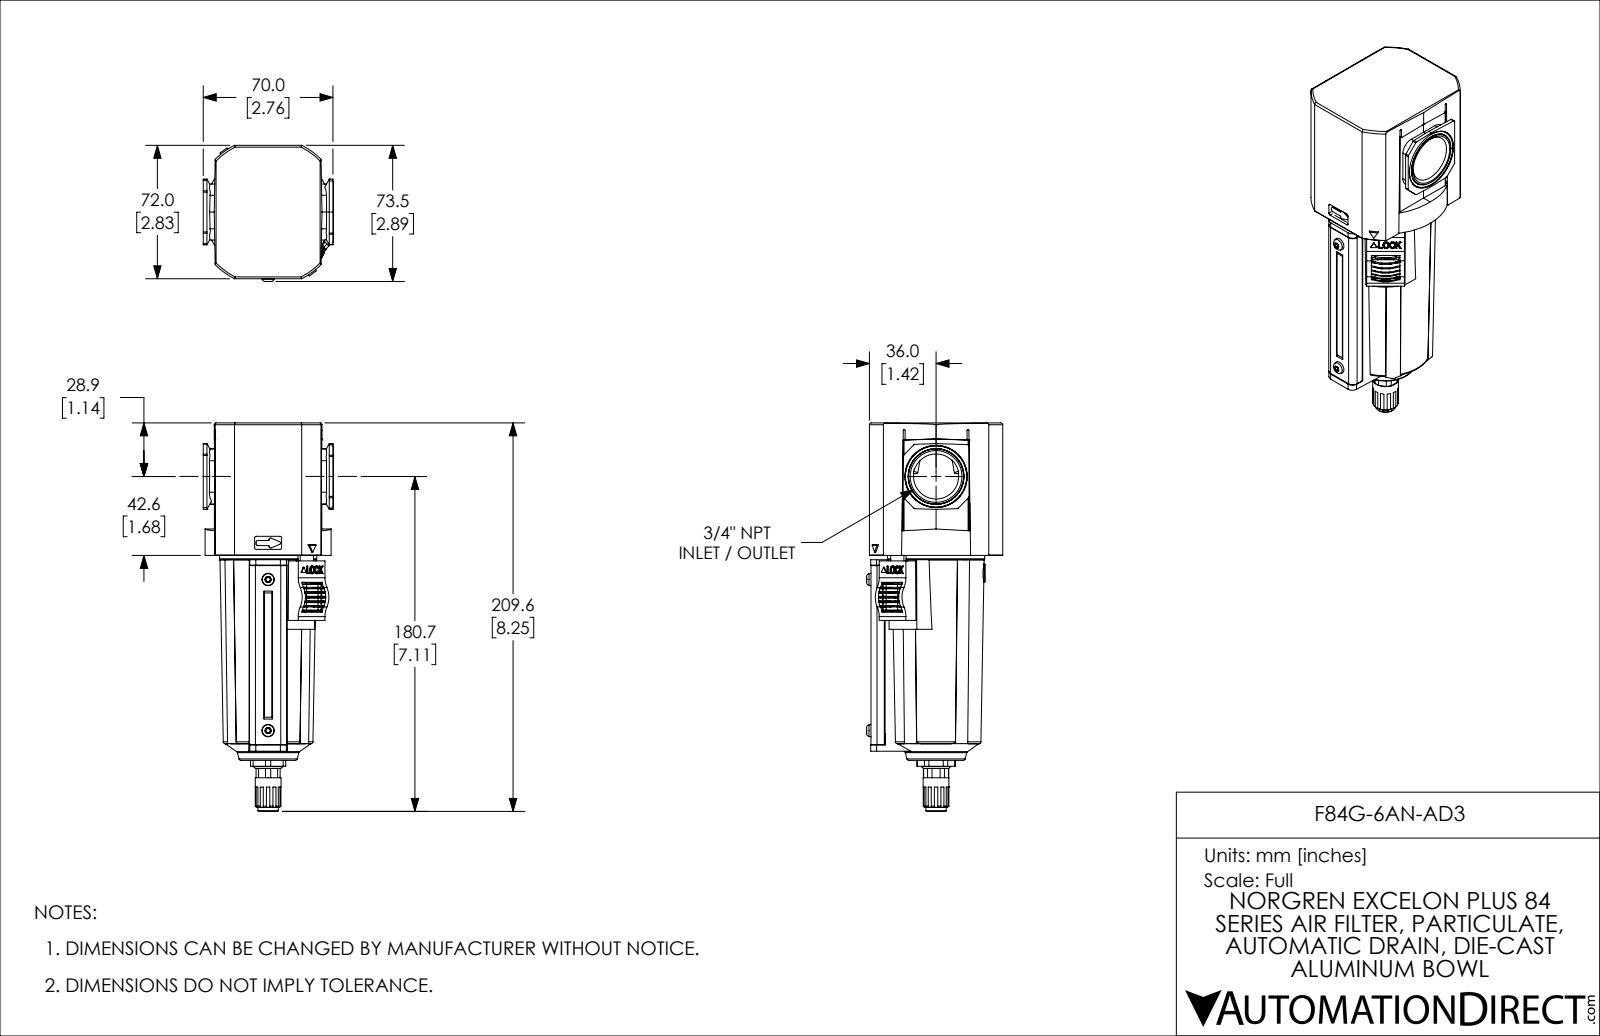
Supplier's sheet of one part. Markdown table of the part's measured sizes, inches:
| quantity | value |
| --- | --- |
| part name | F84G-6AN-AD3 |
| STEP written by | SolidWorks 2021 (CONFIG_CONTROL_DESIGN) |
| units | inches |
| bodies | 6 solids, 1245 faces (552 planar, 453 cylindrical, 240 other) |
| overall size | 8.251 × 2.892 × 2.766 |
| volume | 28.06 in³ |
| surface area | 168.5 in² |
| round holes (diameter × count) | 0.112 × 2, 0.163 × 2, 0.22 × 1, 0.246 × 1, 0.633 × 1, 0.776 × 1, 2.461 × 1 |
| round bosses / shafts (diameter × count) | 0.315 × 2, 0.276 × 2, 0.213 × 2, 2.122 × 1, 2.067 × 1, 2.018 × 1, 1.959 × 1, 1.953 × 1 |
| partial cylindrical surfaces (radius × count) | 0.039 × 58, 0.02 × 37, 0.028 × 28, 0.01 × 18, 0.008 × 8, 0.038 × 8, 0.045 × 8, 0.06 × 8 |
| main face-to-face distances | 0.059, 2.352, 2.411, 2.047, 0.378, 2.457, 2.835, 0.364, 1.988, 2.756 |
| hole center spacings | 0.594, 1.189, 2.504 |
